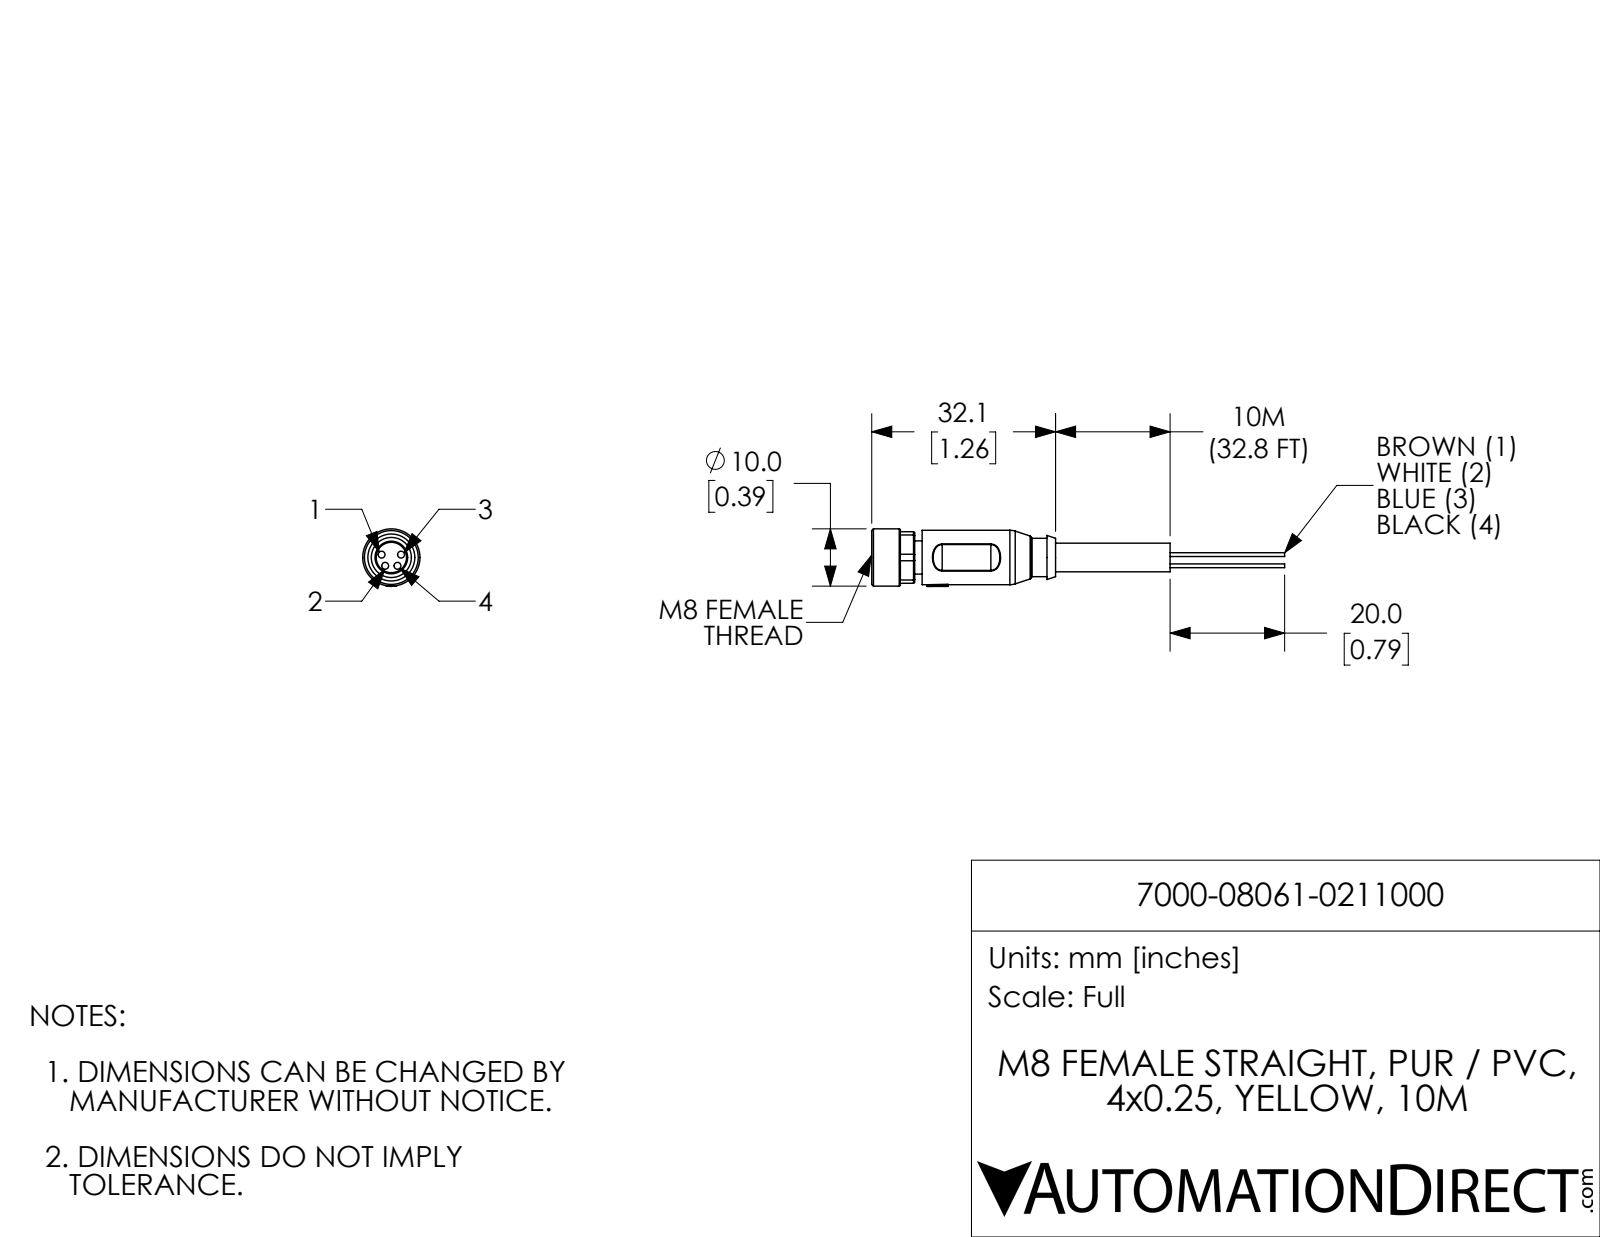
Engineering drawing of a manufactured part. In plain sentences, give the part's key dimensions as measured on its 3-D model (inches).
The part is named "7000-08061-0211000". Its 3-D file was written by "SolidWorks 2017 (AUTOMOTIVE_DESIGN)". It is 1 solid with 115 faces: 38 planar, 46 cylindrical and 31 other. Overall it measures 2.839 by 0.396 by 0.394 inches. Its volume is 0.141 cubic inches and its surface area 2.944 square inches. Round holes: 4 of diameter 0.047, 1 of diameter 0.276. Round bosses or shafts: 4 of diameter 0.026, 1 of diameter 0.394, 1 of diameter 0.374, 1 of diameter 0.264, 1 of diameter 0.228, 1 of diameter 0.224, 1 of diameter 0.197. Partial cylindrical surfaces (rounded edges, fillets, slot ends): 4 of radius 0.008, 4 of radius 0.098, 1 of radius 0.193, 1 of radius 0.199. The main face-to-face distances are 0.327, 0.051, 0.969, 0.354, 0.059, 0.028, 1.756, 1.705, 0.268, 0.319. The hole center spacings are 0.07, 0.071, 0.081, 0.133, 0.084, 0.134.
